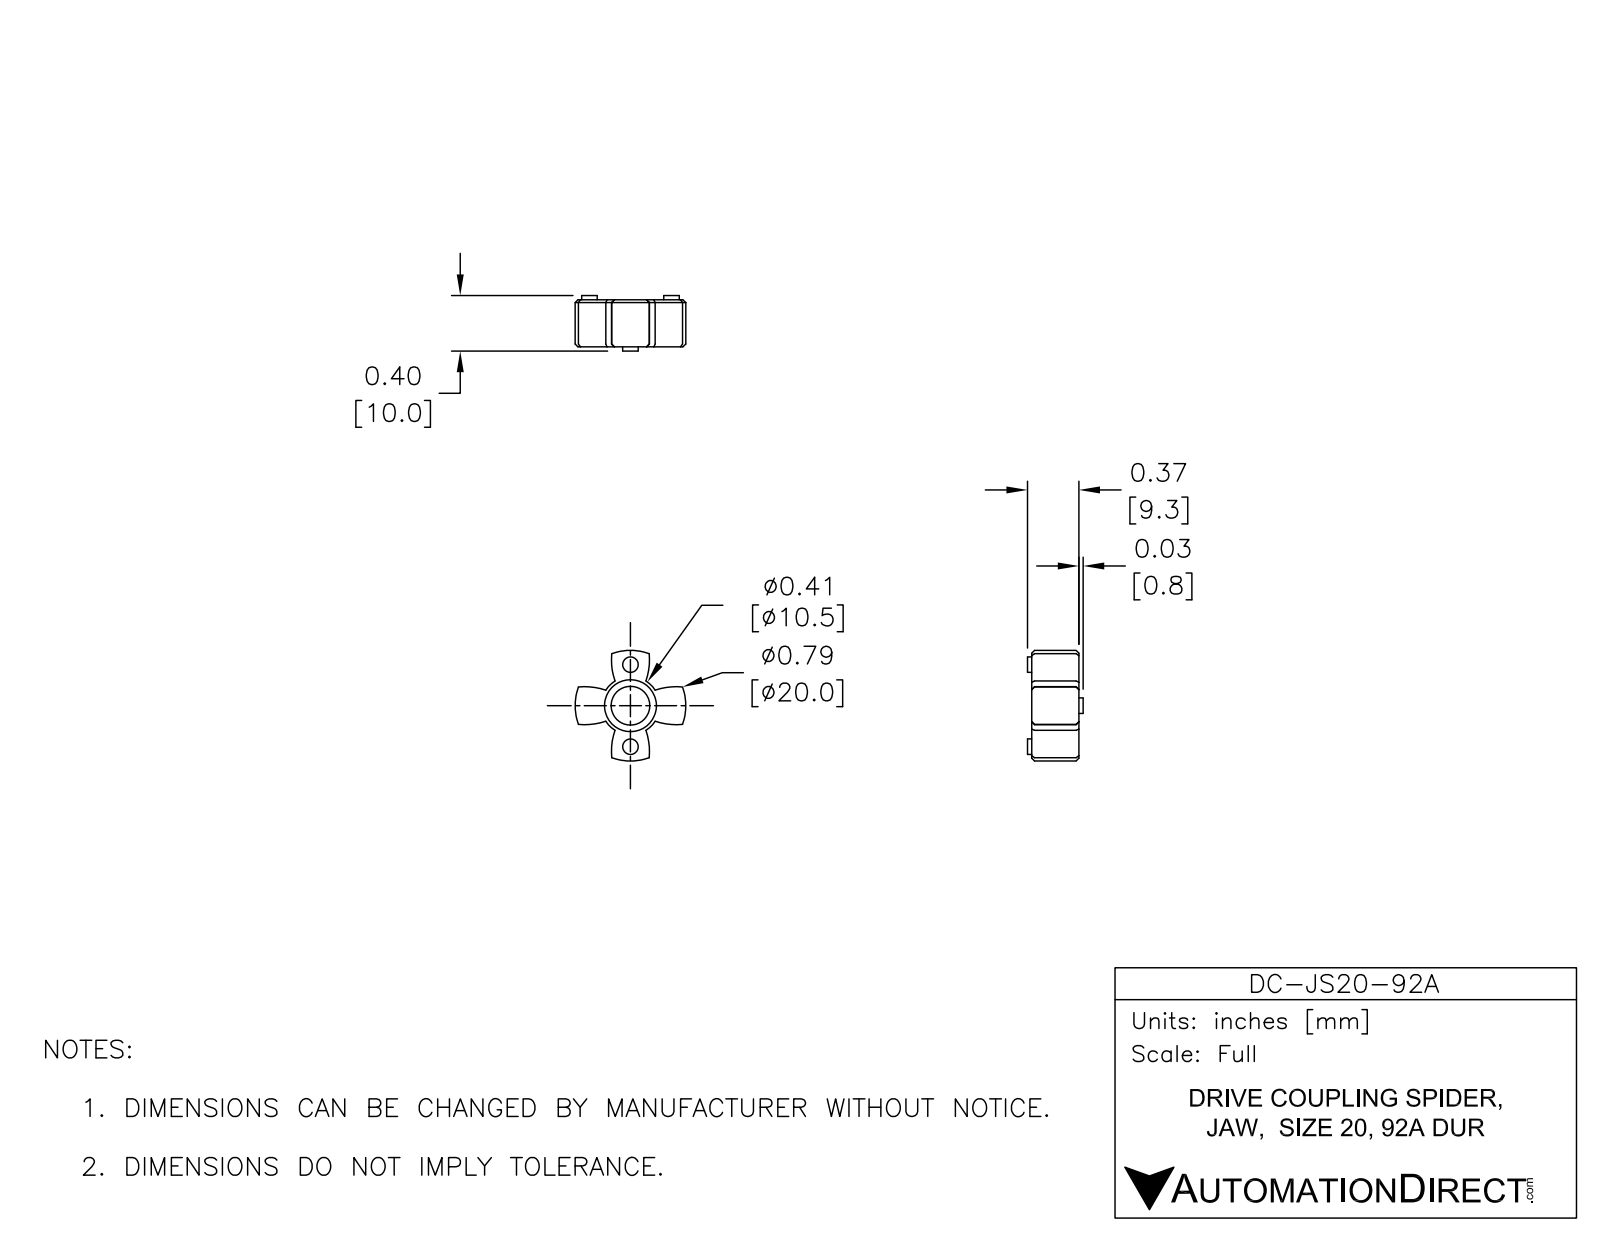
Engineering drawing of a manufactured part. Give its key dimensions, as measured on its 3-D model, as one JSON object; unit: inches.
{"part_name": "DC-JS20-92A", "step_written_by": "SolidWorks 2015 (AUTOMOTIVE_DESIGN)", "units": "inches", "bodies": {"solids": 1, "faces": 81, "planar": 8, "cylindrical": 31, "other": 42}, "overall_size": [0.786, 0.786, 0.395], "volume_in3": 0.093, "surface_area_in2": 1.821, "round_holes": [[0.275, 1]], "round_bosses_or_shafts": [[0.11, 4]], "partial_cylinders_radius": [[0.46, 4], [0.207, 1], [0.393, 1]], "face_to_face_distances": [0.335, 0.125, 0.21, 0.085, 0.03, 0.155, 0.24, 0.365, 0.395]}
